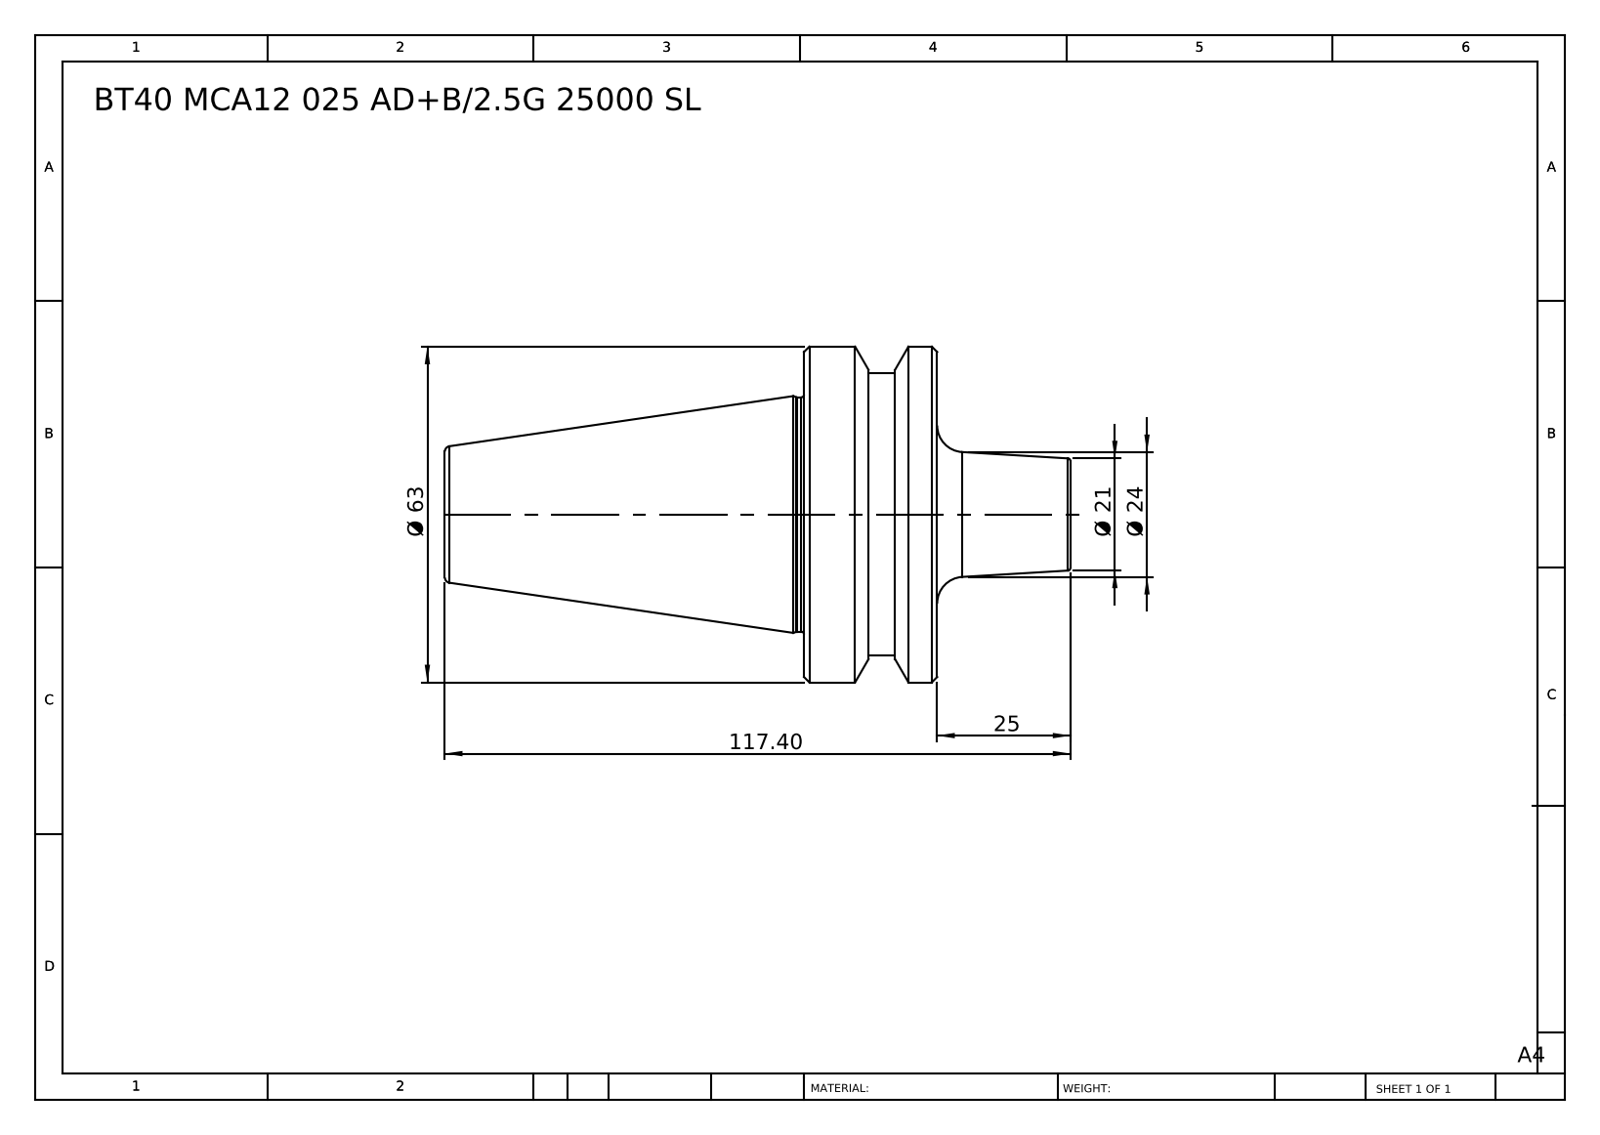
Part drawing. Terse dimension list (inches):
name: BT40 MCA12 025 AD+B-2.5G 25000 SL
written by: SolidWorks 2014 (CONFIG_CONTROL_DESIGN)
unit: in
bodies: 1 solid, 38 faces (6 planar, 8 cylindrical, 24 other)
size: 4.622 × 2.48 × 2.48
volume: 9.073 in³; area: 30.77 in²
bosses: 1× ⌀2.48, 1× ⌀2.087, 1× ⌀1.732
face distances: 0.984, 3.638, 2.654, 1.969, 4.622, 1.492, 0.508, 0.476, 3.13, 1.295
